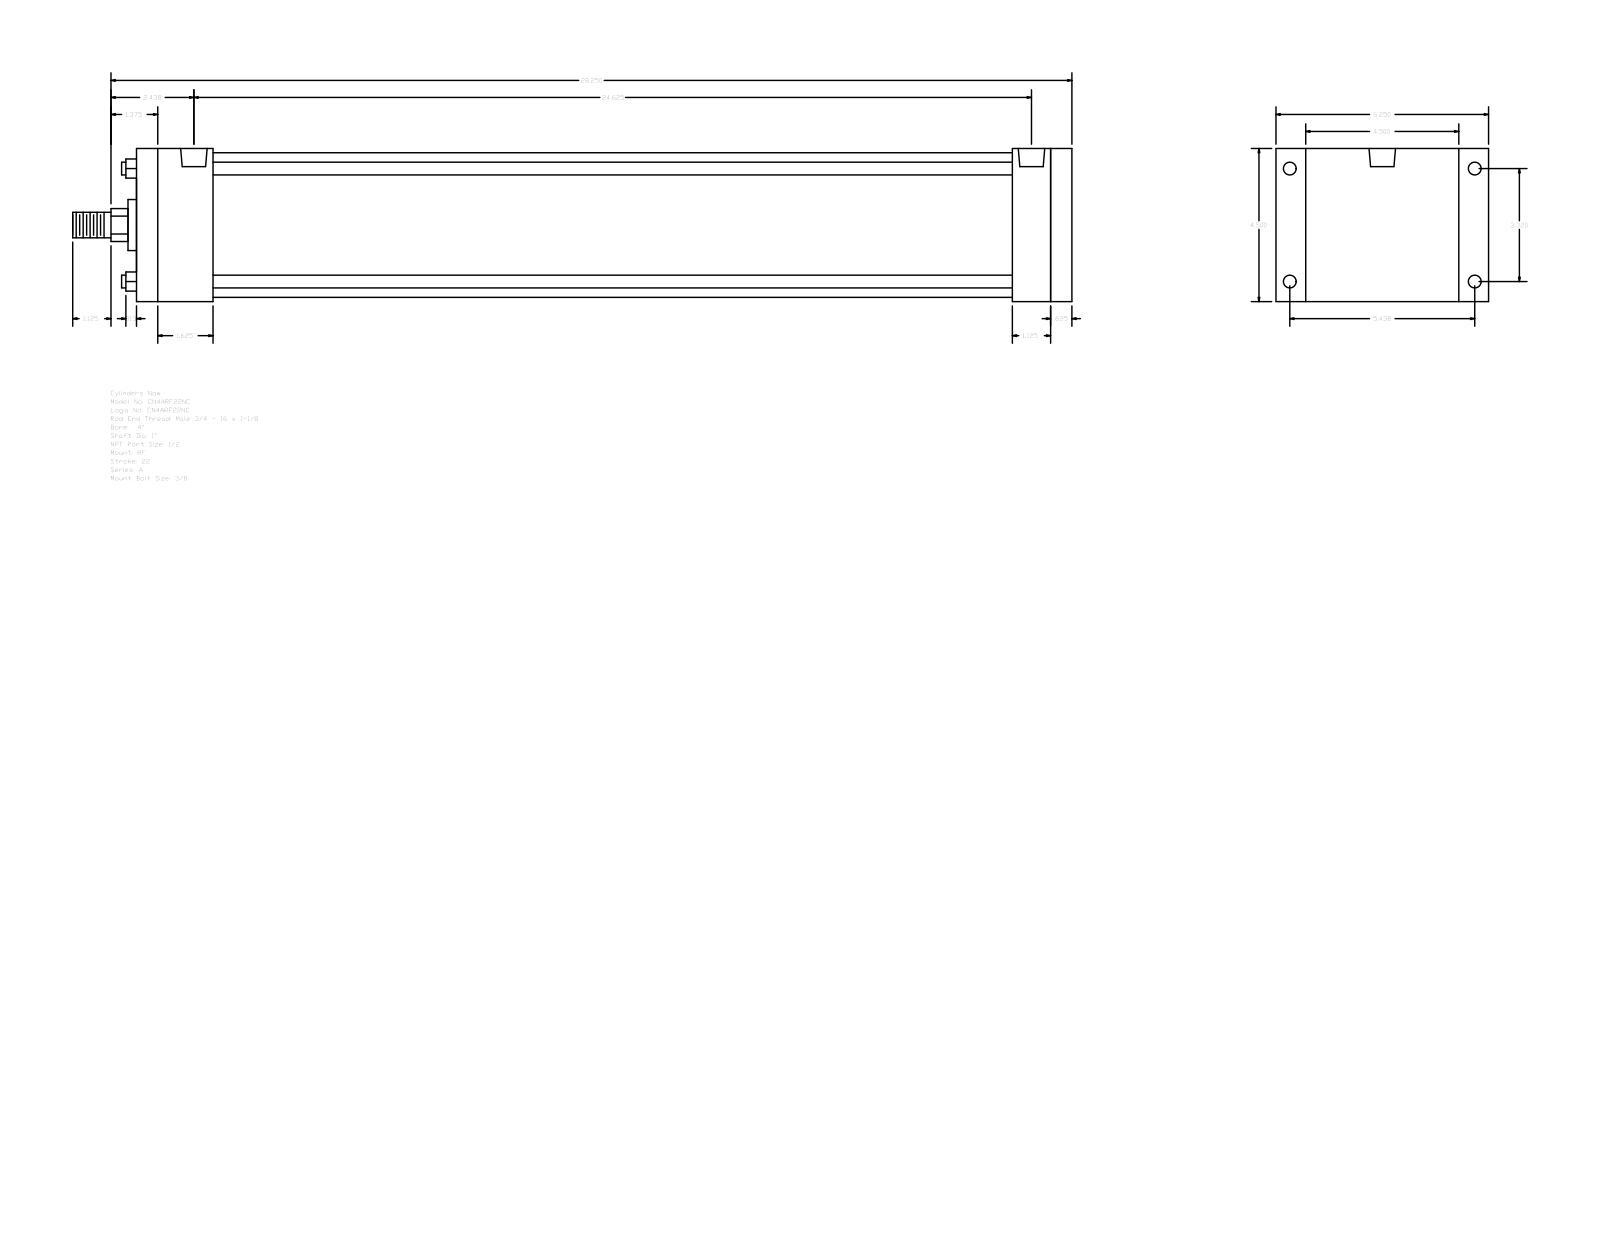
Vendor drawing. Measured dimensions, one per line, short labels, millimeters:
name: A_RF__0400_1
written by: GSSL Pune (CONFIG_CONTROL_DESIGN)
unit: mm
bodies: 0 solids, 92 faces (64 planar, 28 cylindrical, 0 other)
size: 746.12 × 158.75 × 114.3
holes: 4× ⌀8.73, 4× ⌀9.53, 2× ⌀19.77
bosses: 4× ⌀9.53, 1× ⌀107.95, 1× ⌀38.1, 1× ⌀25.4, 1× ⌀19.05
rounds: 1× R12.29
face distances: 114.3, 698.5, 682.62, 15.88, 28.57, 22.23, 136.53, 654.05, 44.45, 57.15
hole spacings: 3.18, 84.32, 138.12, 161.82, 619.12, 622.3, 625.48
